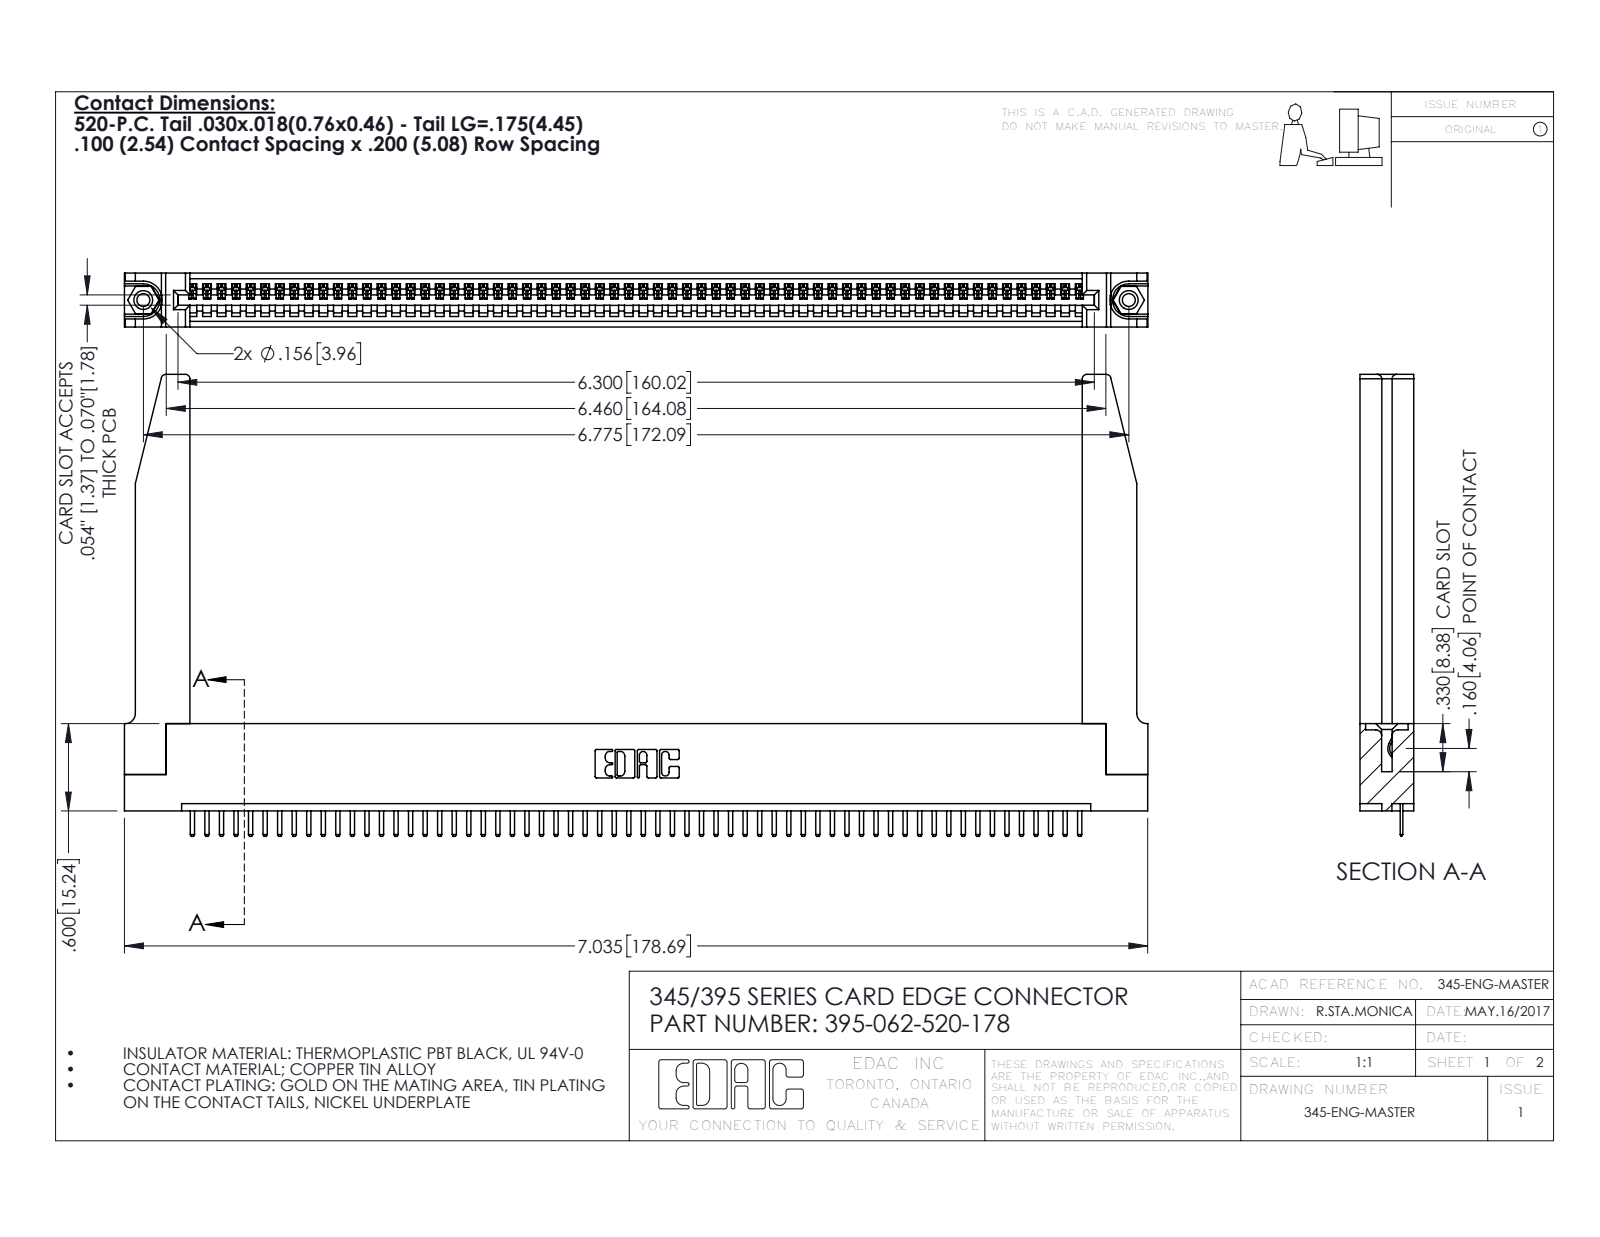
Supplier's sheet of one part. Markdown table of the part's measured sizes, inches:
| quantity | value |
| --- | --- |
| part name | 345-292-001_345-293-120; 395-062-520-178; 345 Part_Flush Mounting Lugs - 0.156 Dia-TH; 345-220-078_345-220-078 (+1 more) |
| STEP written by | SolidWorks 2016 (CONFIG_CONTROL_DESIGN) |
| units | inches |
| bodies | 67 solids, 4204 faces (2826 planar, 1326 cylindrical, 52 other) |
| overall size | 7.036 × 3.175 × 0.37 |
| volume | 1.509 in³ |
| surface area | 45.06 in² |
| round holes (diameter × count) | 0.089 × 2, 0.125 × 2, 0.156 × 2, 0.064 × 1 |
| round bosses / shafts (diameter × count) | 0.155 × 2 |
| partial cylindrical surfaces (radius × count) | 0.01 × 126, 0.006 × 124, 0.01 × 22, 0.03 × 8, 0.007 × 6, 0.031 × 6, 0.026 × 3, 0.031 × 2 |
| main face-to-face distances | 0.37, 0.072, 0.298, 0.2, 0.098, 0.272, 0.025, 0.225, 0.072, 0.148 |
| hole center spacings | 0.27, 6.539, 6.775 |
